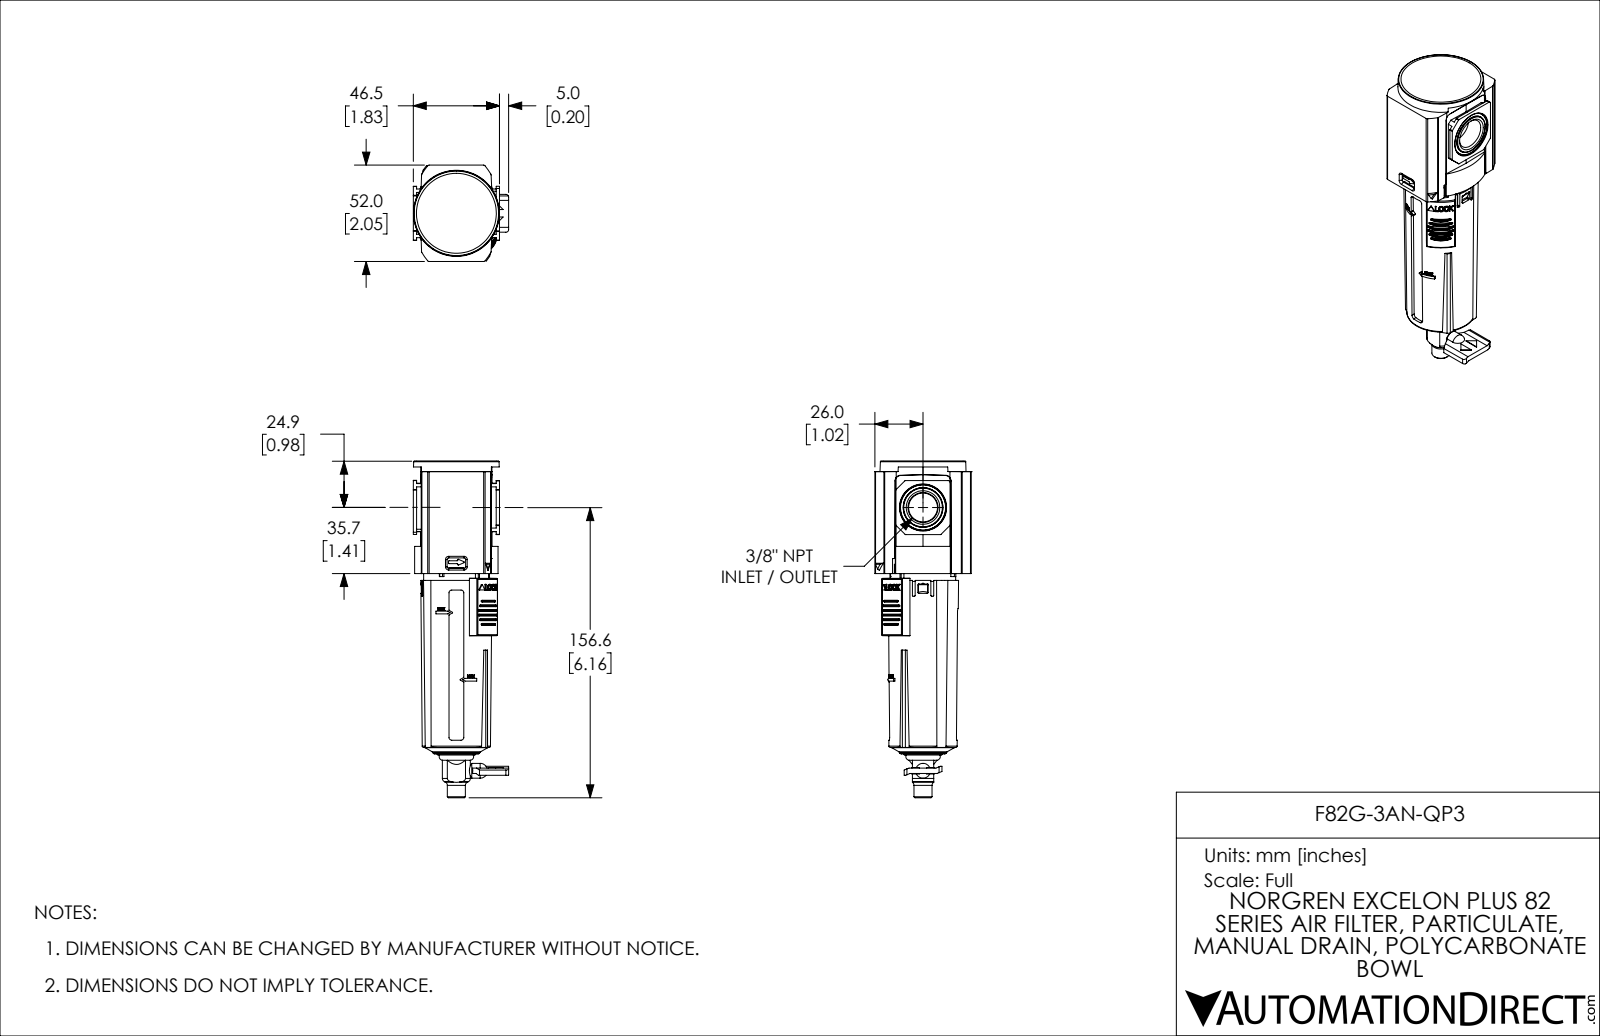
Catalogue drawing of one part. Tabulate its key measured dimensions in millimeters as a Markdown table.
| quantity | value |
| --- | --- |
| part name | F82G-3AN-QP3 |
| STEP written by | SolidWorks 2021 (CONFIG_CONTROL_DESIGN) |
| units | millimeters |
| bodies | 5 solids, 1149 faces (514 planar, 403 cylindrical, 232 other) |
| overall size | 181.6 × 52 × 51.5 |
| volume | 219 100 mm³ |
| surface area | 58 900 mm² |
| round holes (diameter × count) | 3.3 × 2, 6.4 × 1, 16 × 1 |
| round bosses / shafts (diameter × count) | 35.3 × 1, 34.4 × 1, 32.8 × 1, 31.9 × 1, 23 × 1, 15.9 × 1, 9.7 × 1, 8 × 1 |
| partial cylindrical surfaces (radius × count) | 0.5 × 59, 1 × 37, 0.3 × 11, 0.2 × 10, 0.3 × 10, 0.8 × 8, 0.9 × 8, 1.2 × 8 |
| main face-to-face distances | 1.5, 50.5, 37.3, 52, 49, 1.5, 53.2, 54.6, 6, 4.6 |
| hole center spacings | 15.1, 30.2 |
